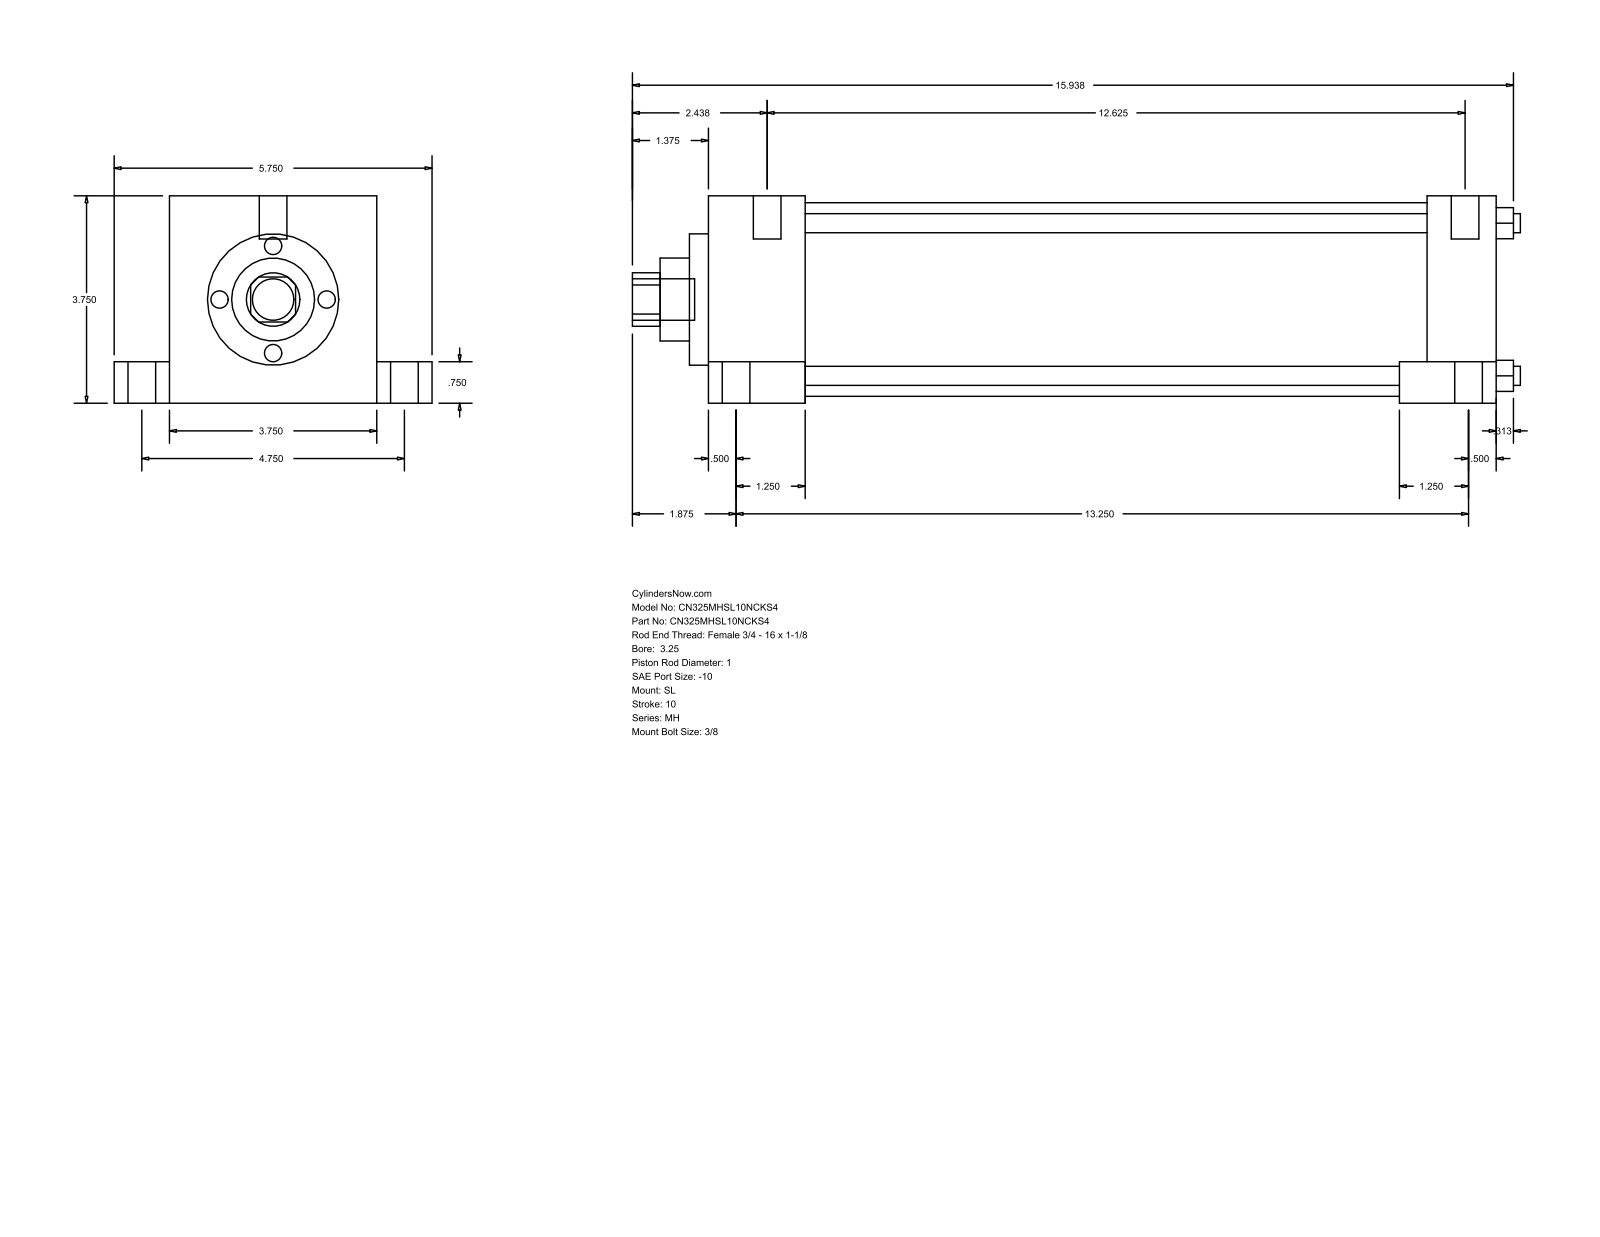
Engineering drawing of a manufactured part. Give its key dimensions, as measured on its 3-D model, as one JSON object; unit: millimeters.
{"part_name": "MH_SL__0325_1", "step_written_by": "GSSL Pune (CONFIG_CONTROL_DESIGN)", "units": "millimeters", "bodies": {"solids": 0, "faces": 110, "planar": 77, "cylindrical": 33, "other": 0}, "overall_size": [407.99, 146.05, 95.25], "round_holes": [[8.76, 4], [25.4, 1], [38.1, 1], [60.33, 1], [88.9, 1]], "round_bosses_or_shafts": [[12.7, 6], [19.05, 5], [5.56, 4]], "partial_cylinders_radius": [[12.29, 1]], "face_to_face_distances": [95.24, 361.96, 44.46, 317.5, 25.41, 120.65, 19.05, 76.19, 330.2, 285.74], "hole_center_spacings": [49.57, 70.1, 99.14]}
